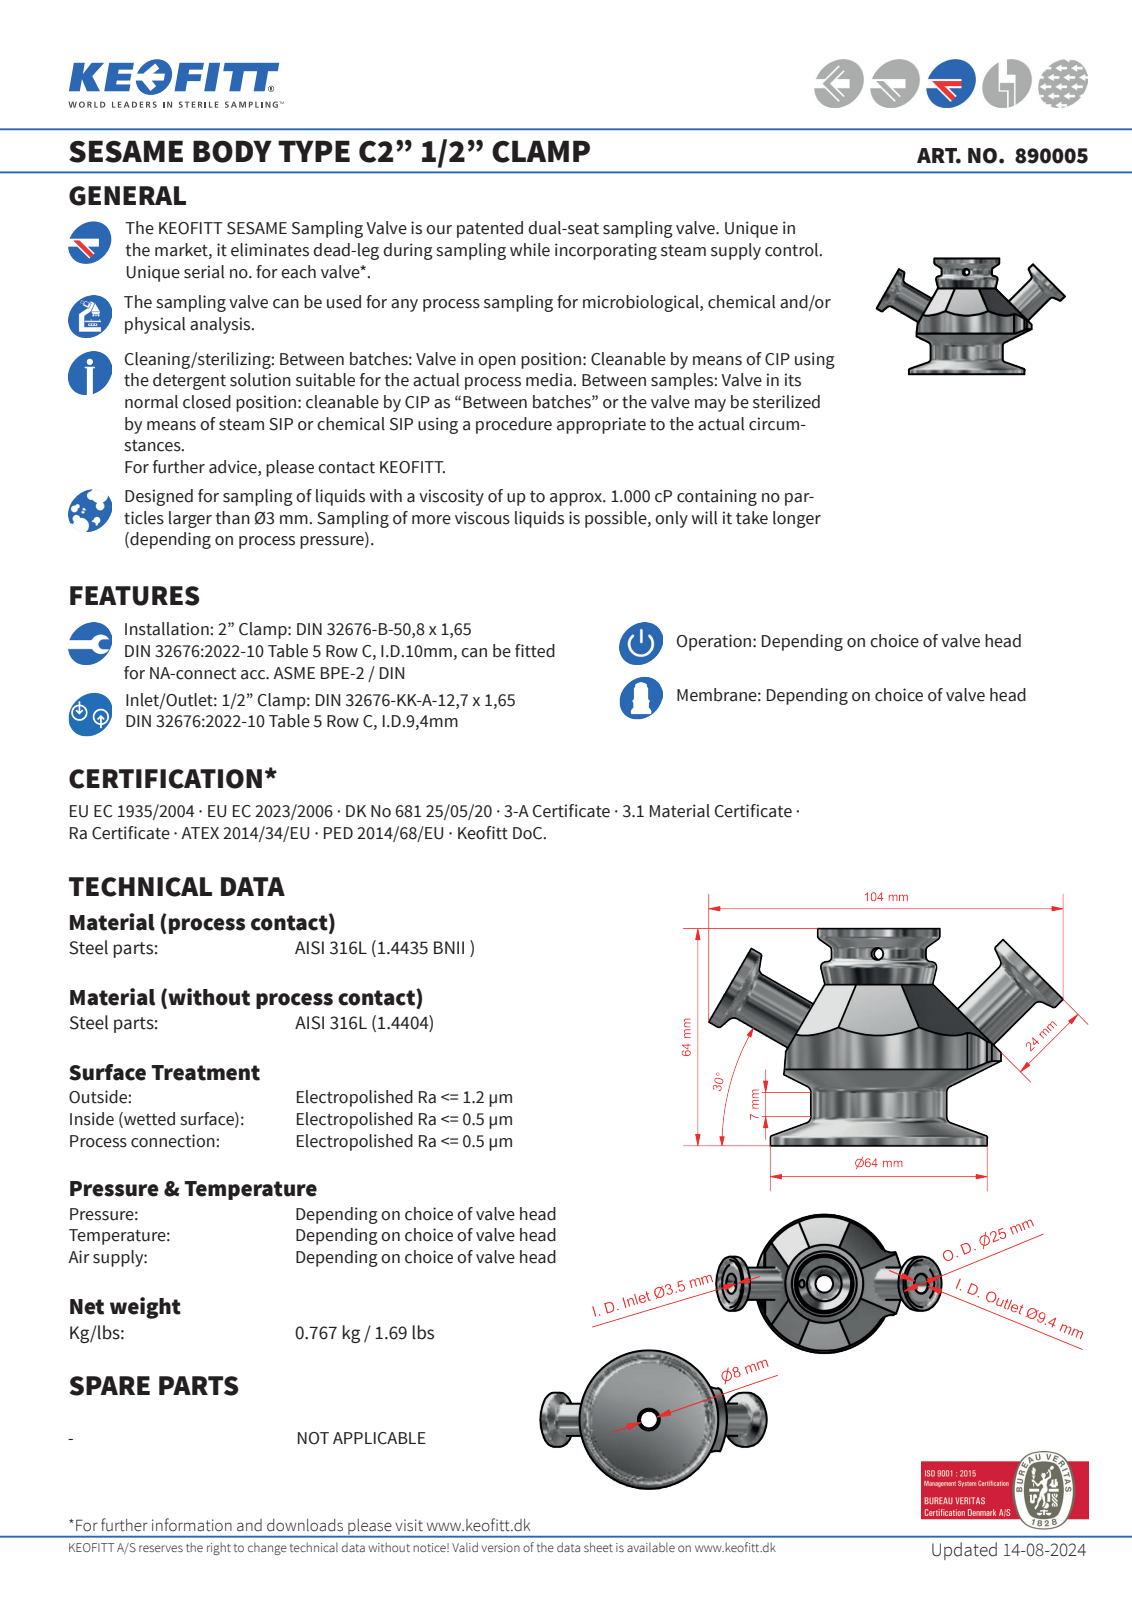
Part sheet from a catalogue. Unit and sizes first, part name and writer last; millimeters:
Units: millimetres
Overall size (bounding box): 104.39 × 64 × 64
Round holes (diameter × count): ⌀3.5 ×3, ⌀21.8 ×2, ⌀8 ×1, ⌀9 ×1, ⌀26 ×1, ⌀29 ×1, ⌀30 ×1
Round bosses / shafts (diameter × count): ⌀25 ×2, ⌀15 ×2, ⌀64 ×1, ⌀40 ×1, ⌀36 ×1, ⌀28.7 ×1, ⌀28.57 ×1, ⌀28.5 ×1
Partial cylindrical surfaces — rounded edges, fillets, slot ends (radius × count): R7 ×2, R31 ×1, R36 ×1
Main face-to-face distances: 51.35, 47.5, 3.85, 64, 16.5, 12.65, 0.8, 9.65, 23.21, 23.2
Volume: 113 594 mm³ · Surface area: 27 424 mm²
Bodies: 2 solids, 100 faces (24 planar, 34 cylindrical, 42 other)
Part name (STEP PRODUCT): 890005
STEP written by: Autodesk Inventor 2020 (AUTOMOTIVE_DESIGN)
